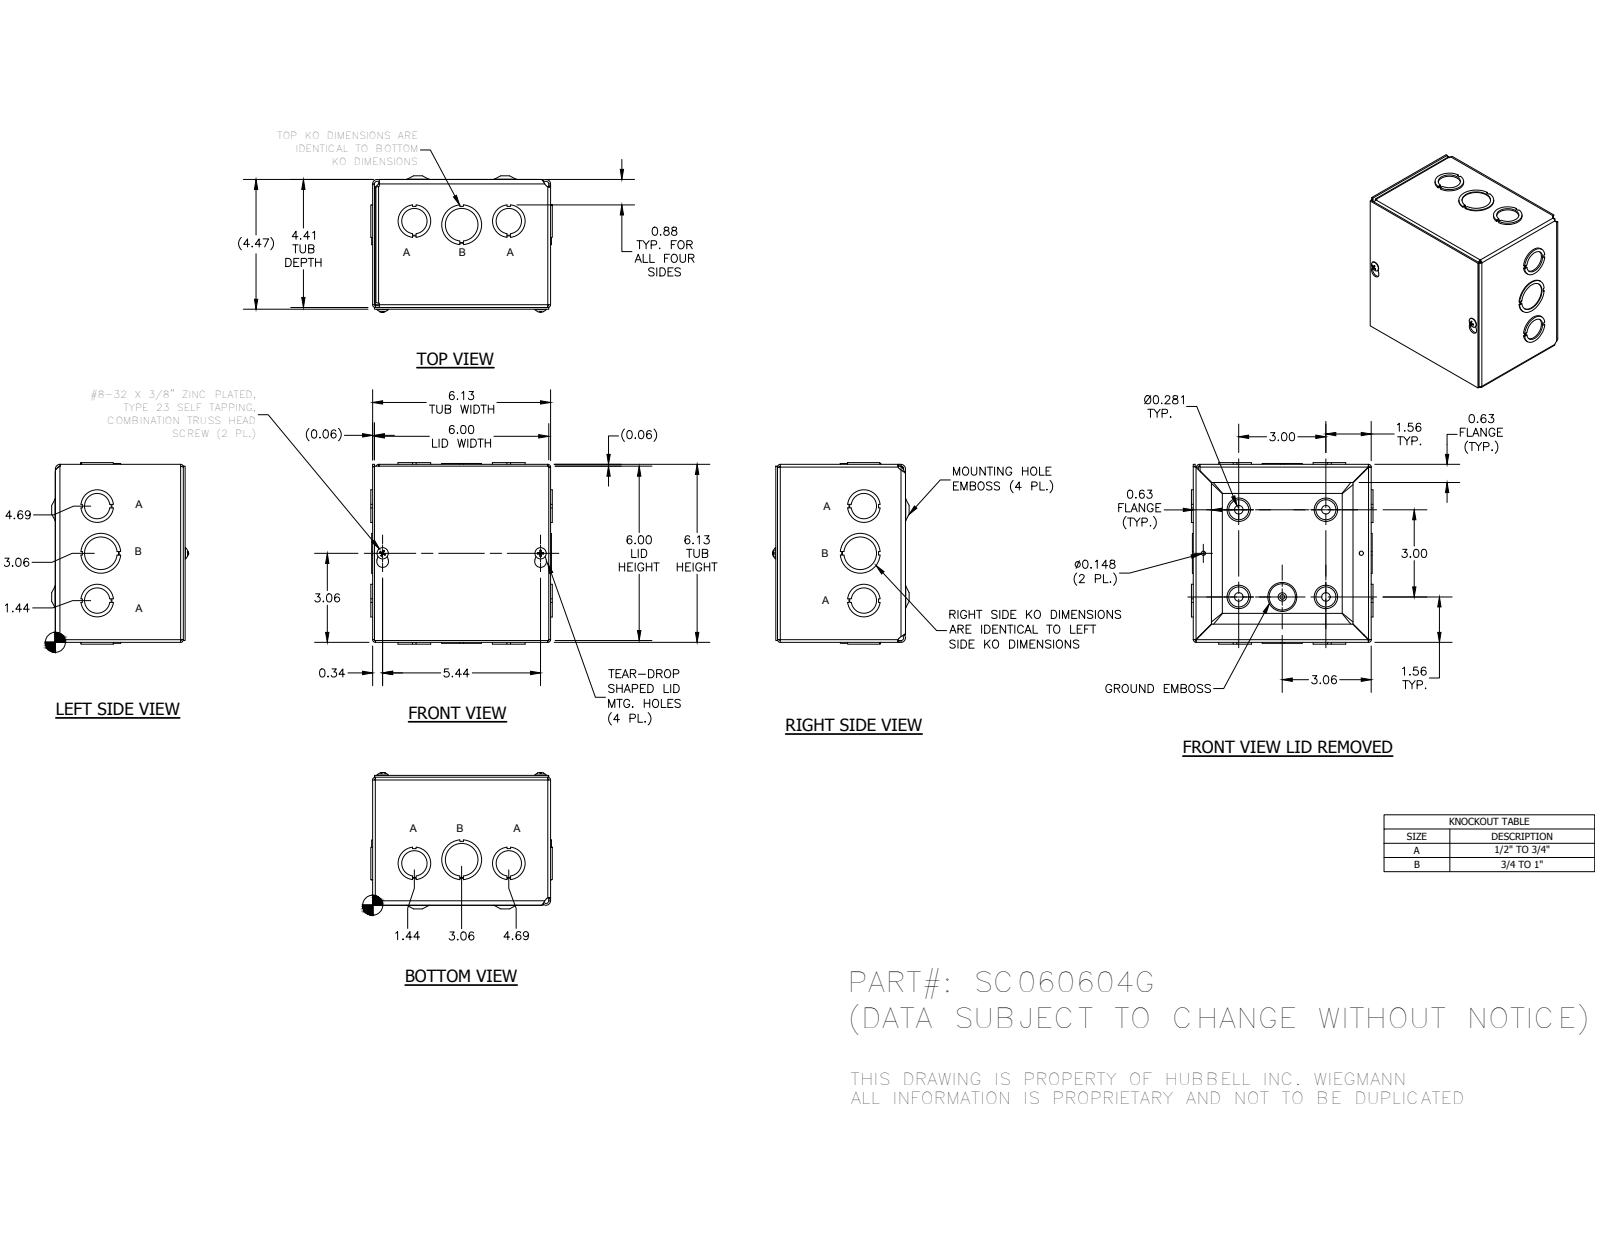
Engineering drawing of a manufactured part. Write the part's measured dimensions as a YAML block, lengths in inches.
part_name: "SC0606GBKP; SC060604GWRA; SC0606GLID; 34056 (+1 more)"
step_written_by: "Autodesk Inventor 2014 (AUTOMOTIVE_DESIGN)"
units: inches
bodies: {solids: 20, faces: 630, planar: 374, cylindrical: 135, other: 121}
overall_size: [6.249, 6.249, 4.693]
round_holes:
  - {diameter: 1.125, count: 6}
  - {diameter: 0.3, count: 4}
  - {diameter: 0.875, count: 4}
  - {diameter: 0.148, count: 2}
  - {diameter: 1.375, count: 2}
  - {diameter: 0.165, count: 1}
round_bosses_or_shafts:
  - {diameter: 0.384, count: 2}
  - {diameter: 0.164, count: 2}
  - {diameter: 0.228, count: 1}
partial_cylinders:
  - {radius: 0.031, count: 8}
  - {radius: 0.093, count: 8}
  - {radius: 0.055, count: 4}
  - {radius: 0.062, count: 4}
  - {radius: 0.094, count: 4}
  - {radius: 0.11, count: 4}
  - {radius: 0.117, count: 4}
  - {radius: 0.124, count: 4}
face_to_face_distances: [0.062, 0.062, 6.125, 4.343, 6.063, 6.063, 6.001, 4.405, 0.063, 4.406]
hole_center_spacings: [1.933, 3, 1.5, 1.63, 1.63, 3.25, 3.354, 4.243]
